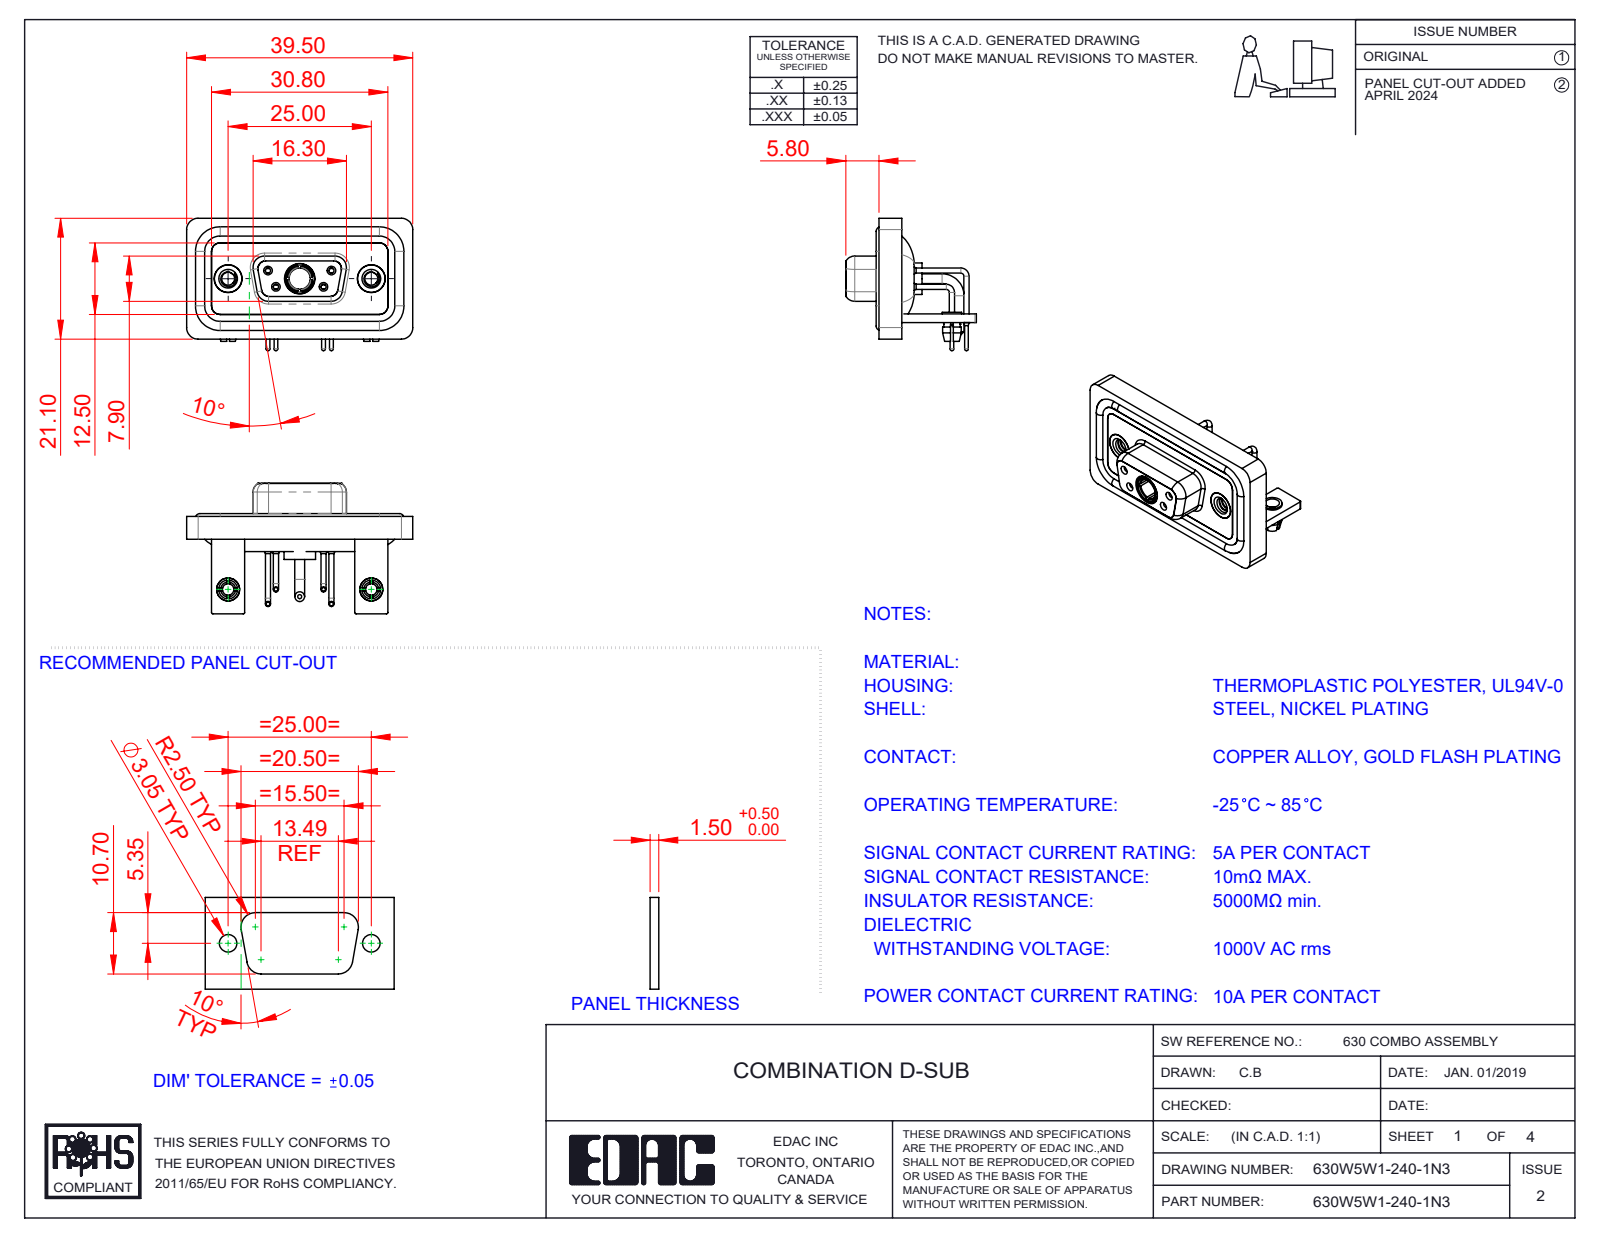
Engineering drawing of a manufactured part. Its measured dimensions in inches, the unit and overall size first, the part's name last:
Units: inches
Overall size (bounding box): 1.555 × 0.91 × 0.898
Round holes (diameter × count): ⌀0.079 ×6, ⌀0.035 ×4, ⌀0.043 ×4, ⌀0.059 ×4, ⌀0.191 ×3, ⌀0.063 ×2, ⌀0.067 ×2, ⌀0.089 ×2, ⌀0.098 ×2, ⌀0.126 ×2, ⌀0.157 ×2, ⌀0.159 ×2
Round bosses / shafts (diameter × count): ⌀0.063 ×6, ⌀0.035 ×4, ⌀0.026 ×4, ⌀0.195 ×2, ⌀0.189 ×2, ⌀0.157 ×2, ⌀0.134 ×2, ⌀0.13 ×2
Partial cylindrical surfaces — rounded edges, fillets, slot ends (radius × count): R0.079 ×19, R0.059 ×18, R0.01 ×16, R0.053 ×8, R0.063 ×8, R0.02 ×5, R0.024 ×4, R0.026 ×4
Main face-to-face distances: 0.016, 0.114, 0.059, 0.071, 0.043, 0.146, 0.063, 0.031, 0.098, 0.122
Hole centre spacings: 0.124, 0.225, 0.28, 0.492, 0.713, 0.984, 0.173, 0.173
Volume: 0.316 in³ · Surface area: 13.54 in²
Bodies: 17 solids, 816 faces (262 planar, 361 cylindrical, 193 other)
Part name (STEP PRODUCT): Power Socket_10A RA; 630Combo Waterproof Housing_09 Contacts; 630Combo Threaded Rivet_2; 630Combo Stabilizer Bracket_50 Contacts (+7 more)
STEP written by: SolidWorks 2023 (CONFIG_CONTROL_DESIGN)
